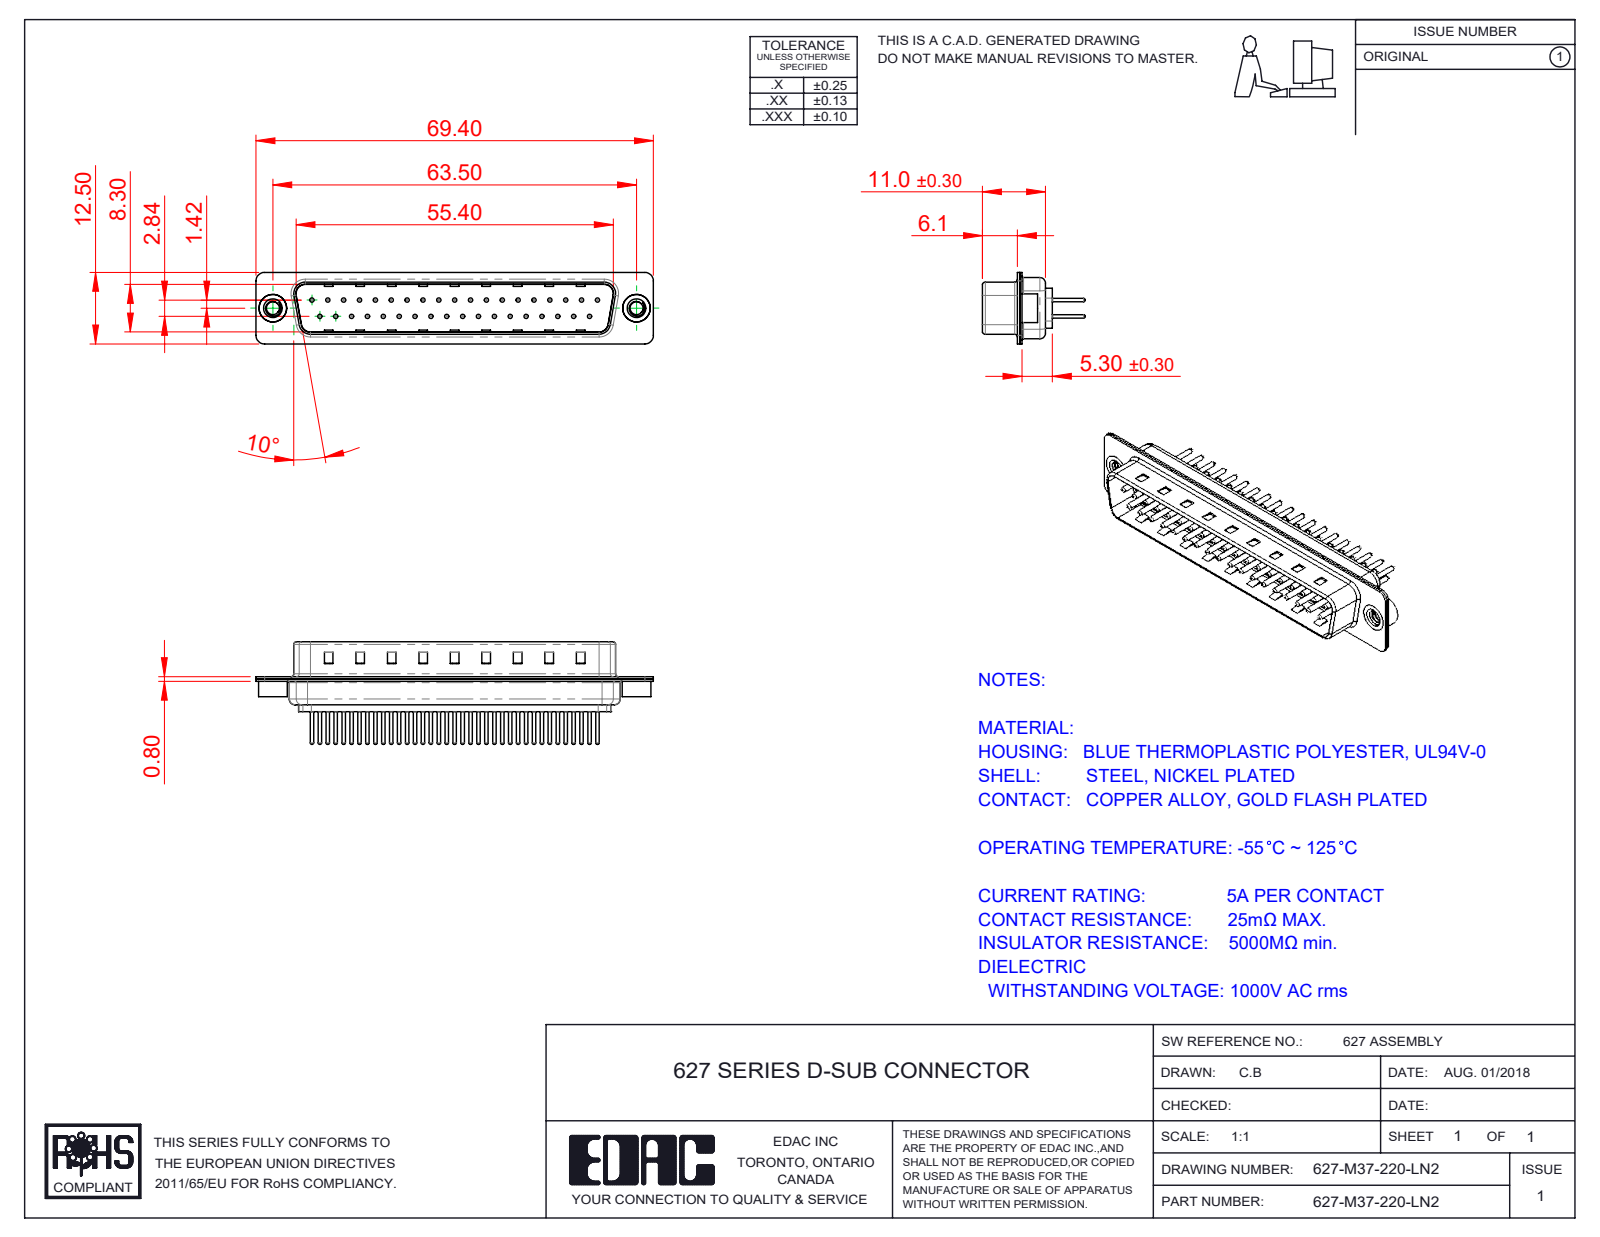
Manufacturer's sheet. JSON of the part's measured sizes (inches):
{"part_name": "627M Housing_37 Contacts; 627-M37-220-LN2; 627M Shell Front_37 Contacts; 627M Contact Row 2_20 (+3 more)", "step_written_by": "SolidWorks 2020 (CONFIG_CONTROL_DESIGN)", "units": "inches", "bodies": {"solids": 42, "faces": 1781, "planar": 462, "cylindrical": 659, "other": 660}, "overall_size": [2.732, 0.705, 0.492], "volume_in3": 0.23, "surface_area_in2": 14.37, "round_holes": [[0.03, 37], [0.063, 37], [0.079, 37], [0.089, 2], [0.157, 2], [0.189, 2]], "round_bosses_or_shafts": [[0.059, 37], [0.024, 37], [0.197, 2], [0.193, 2]], "partial_cylinders_radius": [[0.059, 16], [0.079, 12], [0.02, 8], [0.063, 8], [0.01, 4], [0.024, 4], [0.026, 4], [0.035, 4]], "face_to_face_distances": [0.016, 0.031, 0.374, 0.358, 0.343, 0.39, 0.047, 0.224, 0.03, 0.014], "hole_center_spacings": [0.109, 0.218, 0.124, 0.327, 0.436, 0.545, 0.654, 0.763]}
